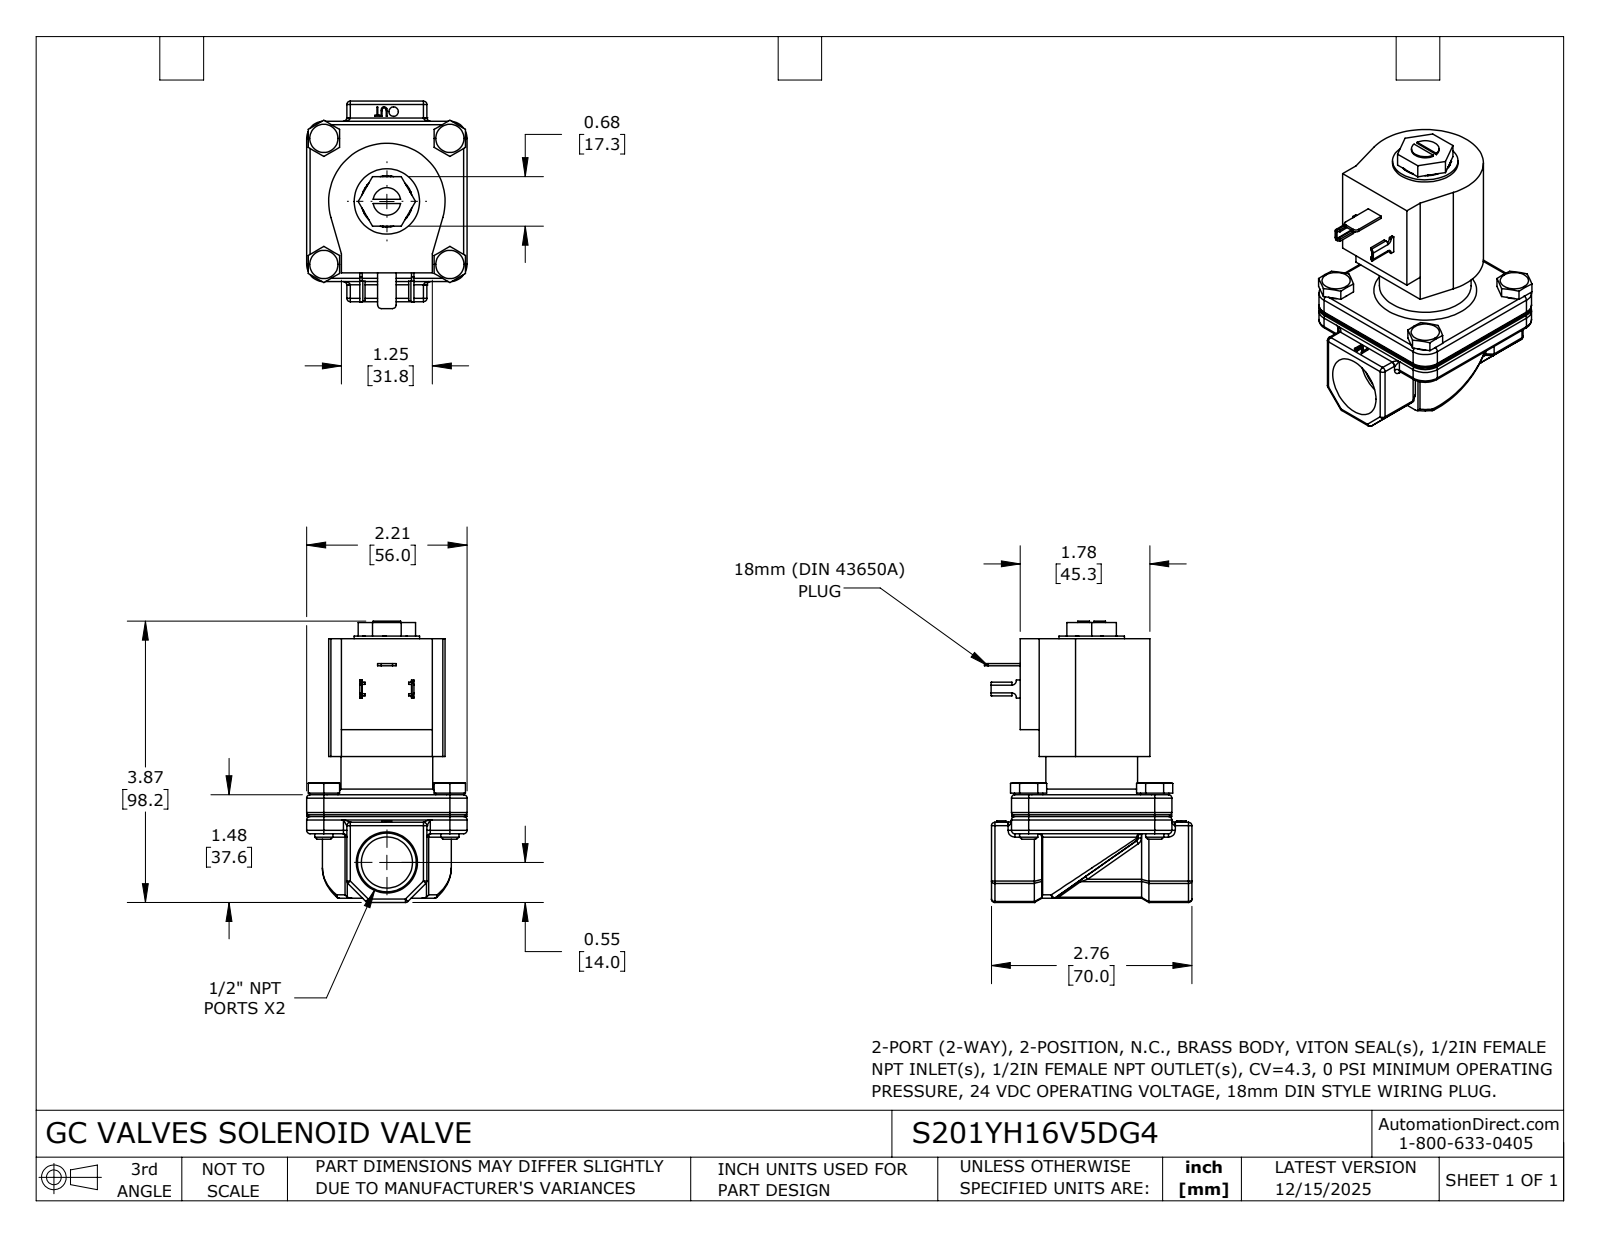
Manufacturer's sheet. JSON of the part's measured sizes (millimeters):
{"part_name": "S201YH16V5DG4", "step_written_by": "SolidWorks 2024 (CONFIG_CONTROL_DESIGN)", "units": "millimeters", "bodies": {"solids": 1, "faces": 507, "planar": 201, "cylindrical": 158, "other": 148}, "overall_size": [98.2, 72.4, 56], "volume_mm3": 154400, "surface_area_mm2": 27620, "round_holes": [[17.9, 1], [17.9, 1]], "round_bosses_or_shafts": [[9.9, 4], [6.4, 4], [32, 1], [22.9, 1], [11.8, 1], [9.7, 1]], "partial_cylinders_radius": [[1.2, 64], [0.2, 4], [0.8, 4], [1, 4], [5.9, 4], [6, 4], [1.3, 2], [1.5, 2]], "face_to_face_distances": [54.4, 1.5, 14, 42, 13.6, 68.1, 56, 26.9, 13.3, 41.1]}
